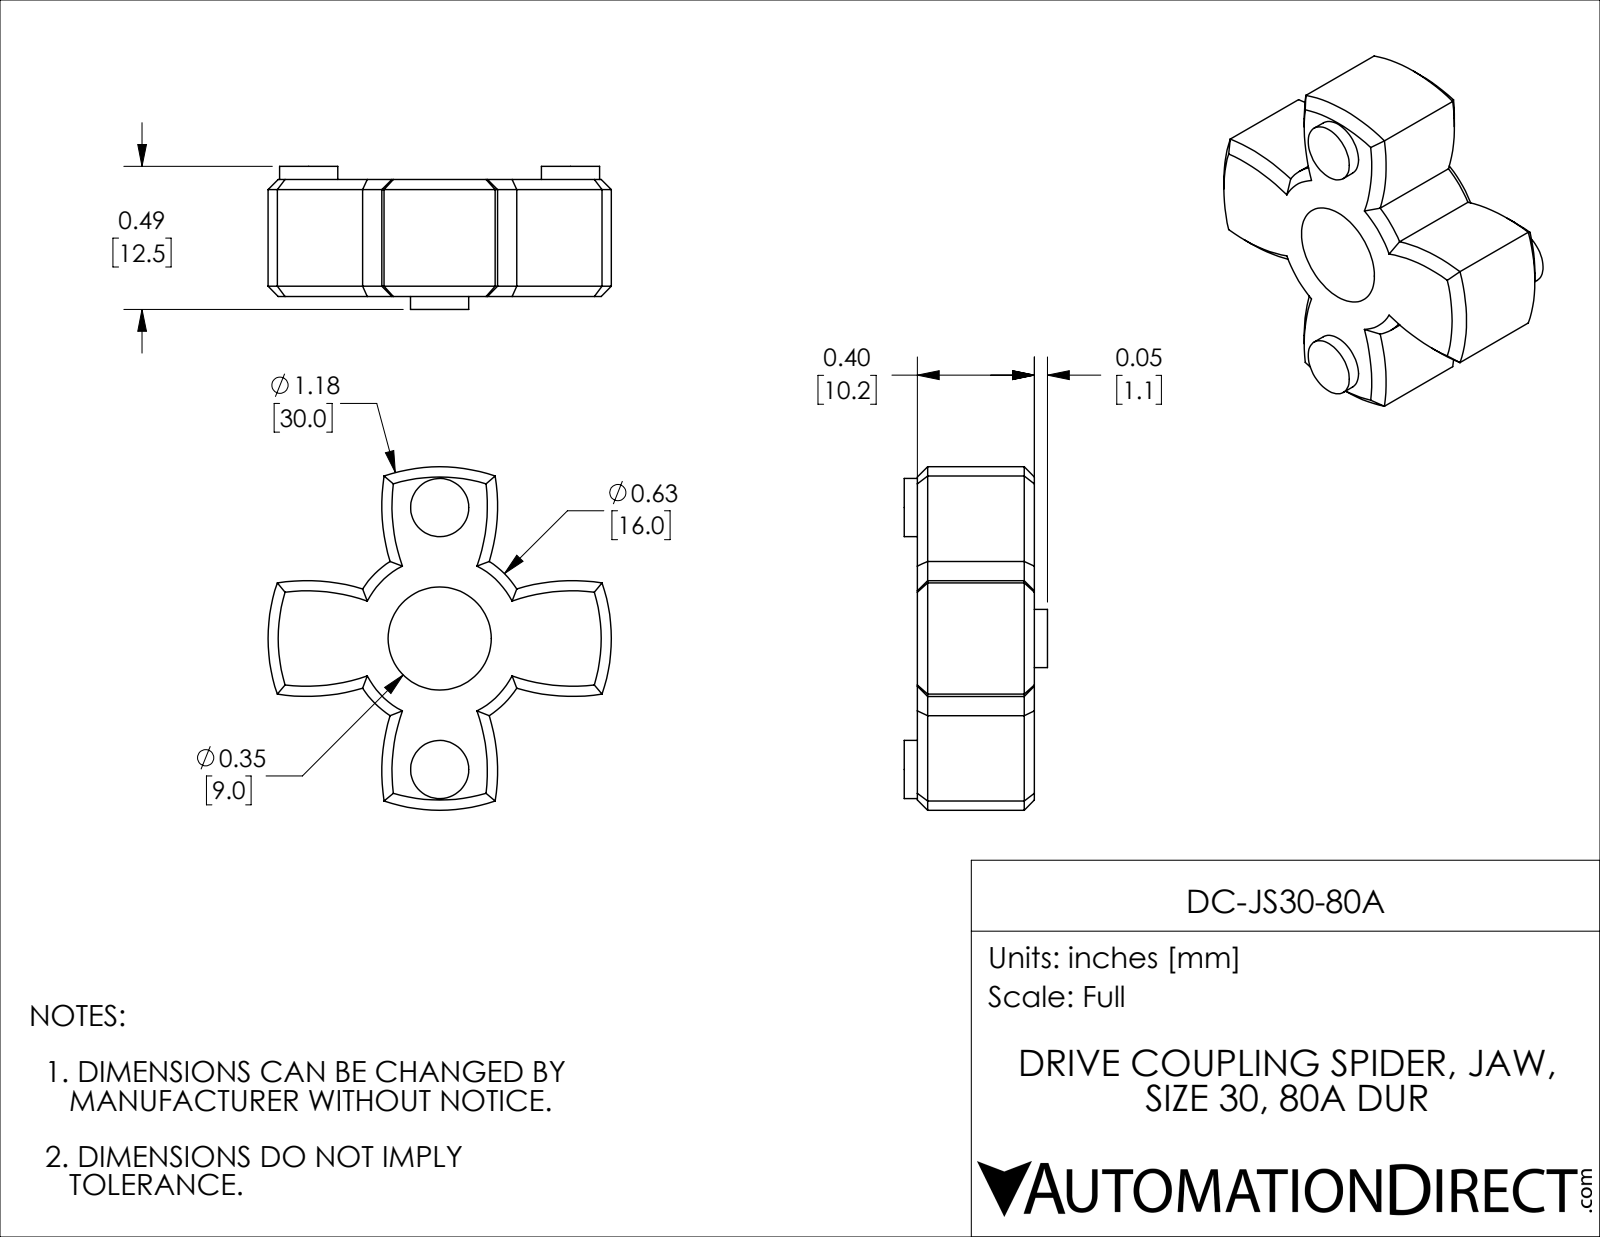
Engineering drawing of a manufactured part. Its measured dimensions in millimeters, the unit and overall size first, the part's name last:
Units: millimetres
Overall size (bounding box): 29.97 × 29.97 × 12.5
Round holes (diameter × count): ⌀9 ×1
Round bosses / shafts (diameter × count): ⌀5.08 ×4
Partial cylindrical surfaces — rounded edges, fillets, slot ends (radius × count): R16.64 ×4, R8 ×1, R14.99 ×1
Main face-to-face distances: 10.22, 1.14, 11.36, 12.5
Volume: 4 285 mm³ · Surface area: 2 239 mm²
Bodies: 1 solid, 73 faces (6 planar, 29 cylindrical, 38 other)
Part name (STEP PRODUCT): DC-JS30-80A
STEP written by: SolidWorks 2019 (AUTOMOTIVE_DESIGN)
